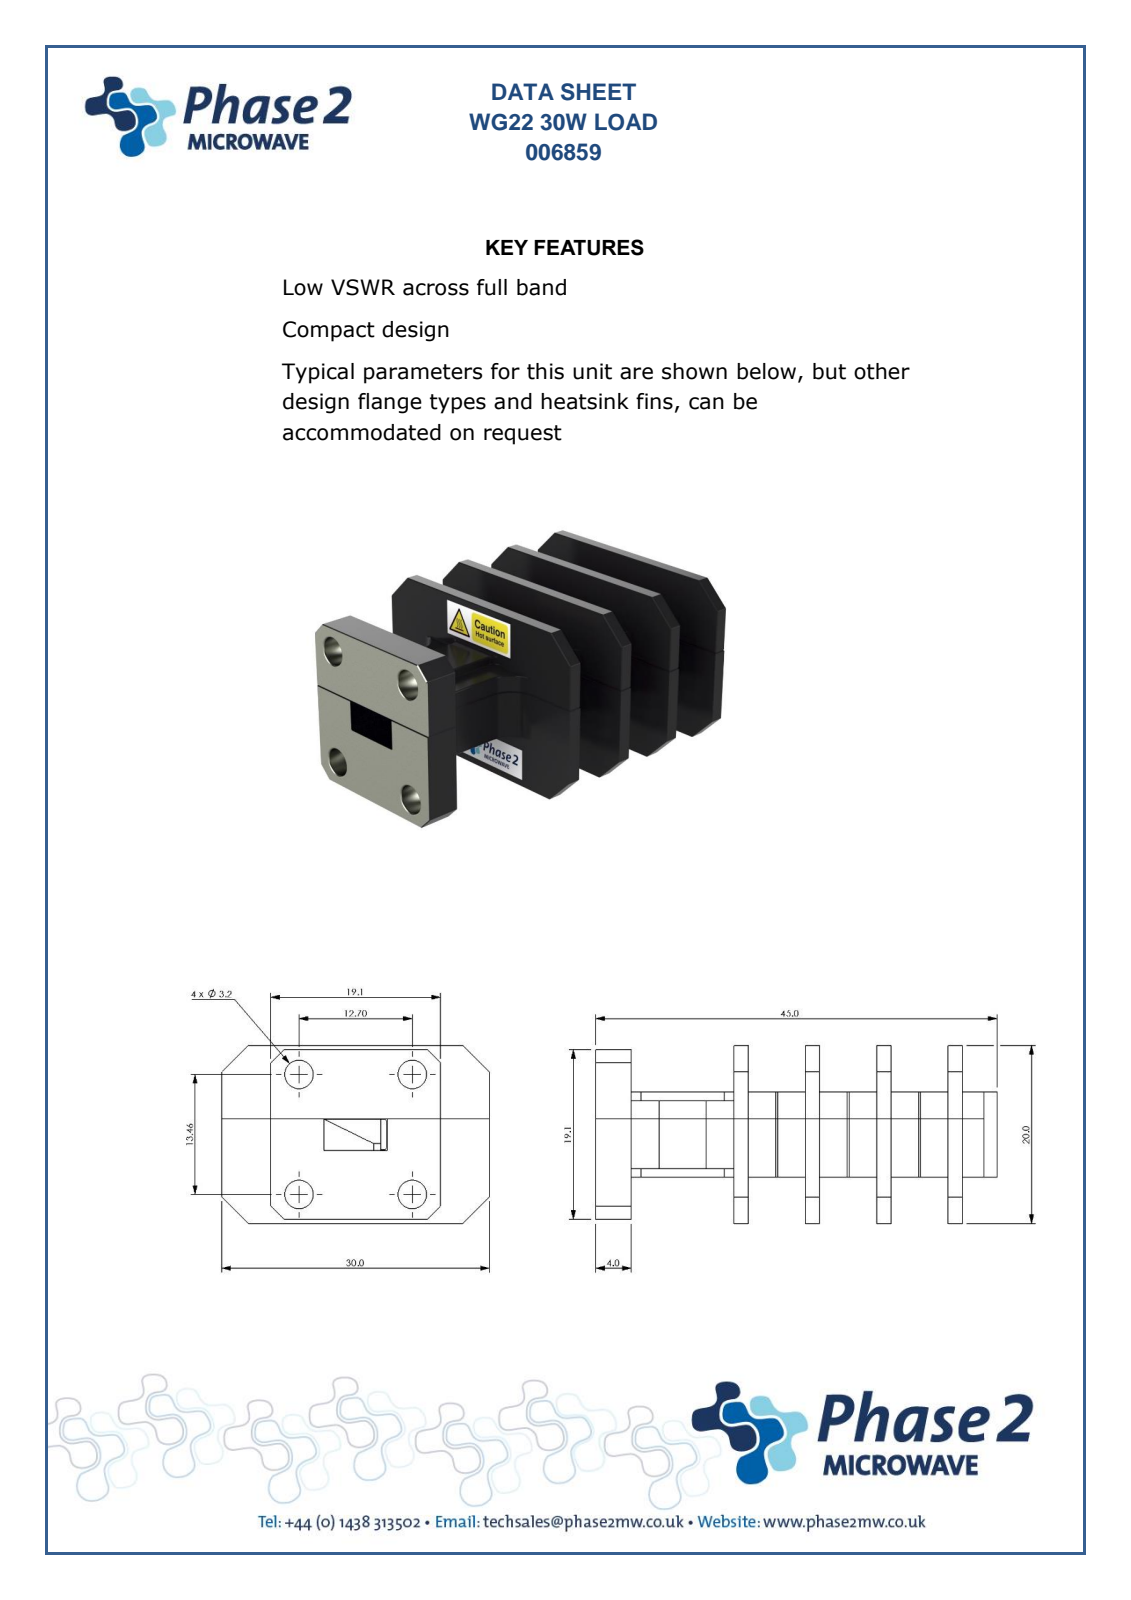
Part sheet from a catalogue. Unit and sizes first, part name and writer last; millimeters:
Units: millimetres
Overall size (bounding box): 45 × 30 × 20
Round holes (diameter × count): ⌀3.2 ×4
Partial cylindrical surfaces — rounded edges, fillets, slot ends (radius × count): R1.1 ×8, R3.1 ×6, R1 ×2
Main face-to-face distances: 25.6, 20, 8.22, 11.78, 30, 41.1, 15.5, 31.1, 3, 37.1
Hole centre spacings: 12.7, 13.46, 18.51
Bodies: 0 solids, 93 faces (61 planar, 31 cylindrical, 1 other)
Part name (STEP PRODUCT): 006859
STEP written by: SolidWorks 2019 (CONFIG_CONTROL_DESIGN)
